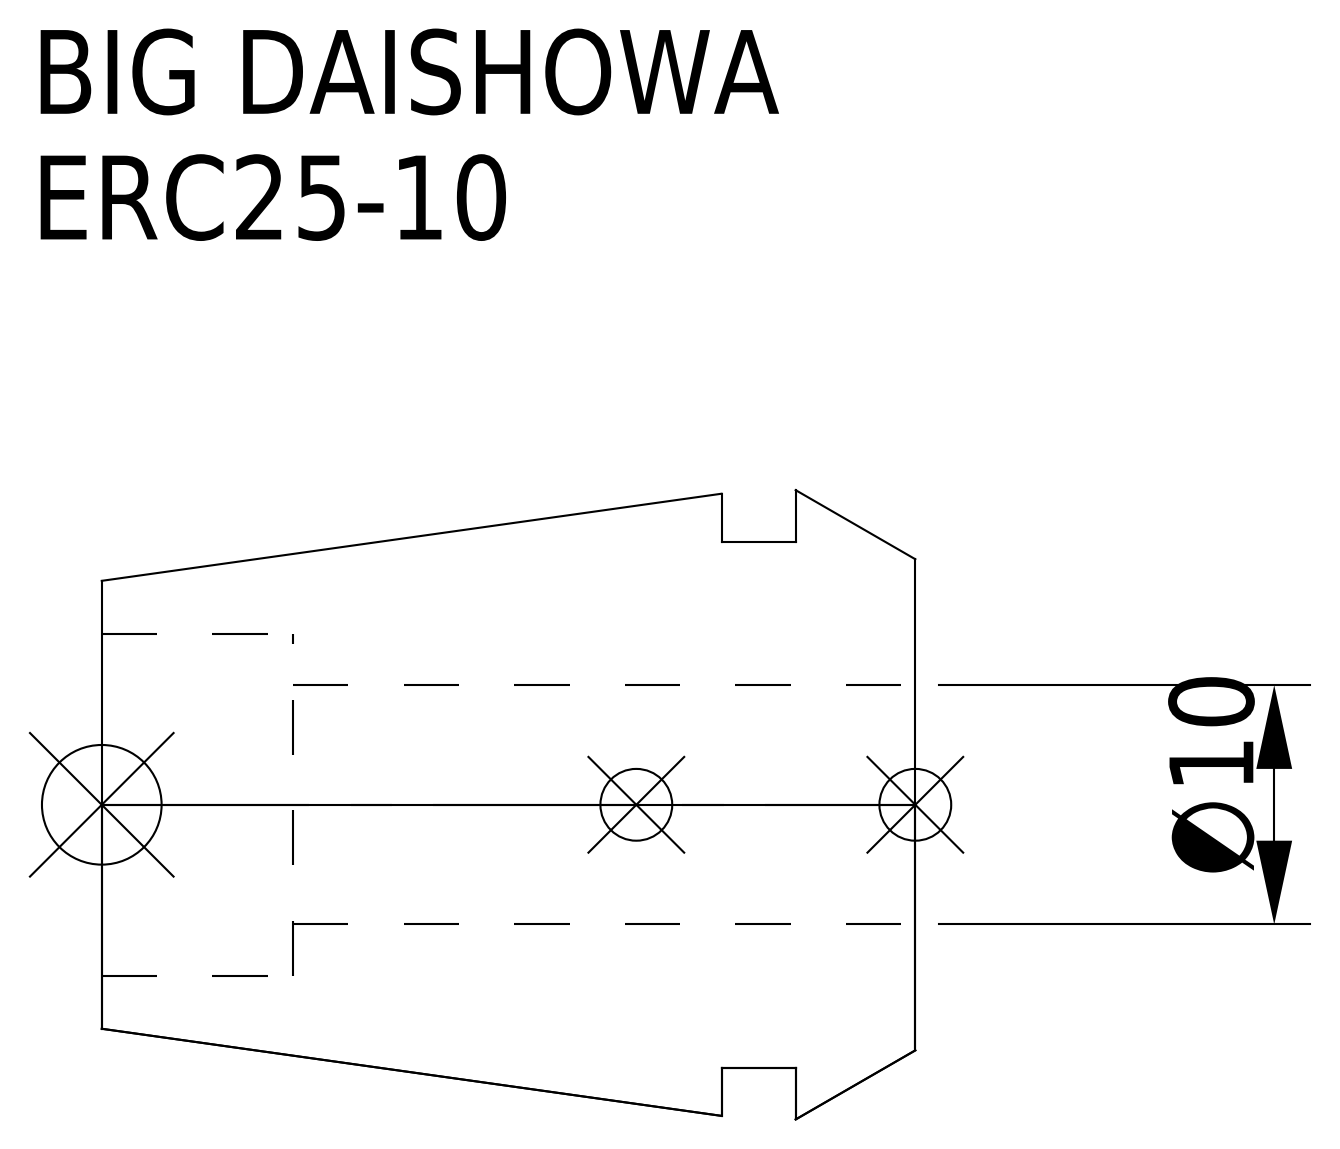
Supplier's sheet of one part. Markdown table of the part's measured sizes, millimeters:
| quantity | value |
| --- | --- |
| part name | ERC25-10 |
| STEP written by | CREO PARAMETRIC BY PTC INC, 2016380 (AUTOMOTIVE_DESIGN) |
| units | millimeters |
| bodies | 1 solid, 15 faces (5 planar, 6 cylindrical, 4 other) |
| overall size | 34 × 26.3 × 26.3 |
| volume | 10 276 mm³ |
| surface area | 4 415 mm² |
| round holes (diameter × count) | 10 × 1, 14.3 × 1 |
| round bosses / shafts (diameter × count) | 22 × 1 |
| main face-to-face distances | 5, 8.1, 3.1, 34, 29, 25.9, 26, 21, 17.9, 8 |
